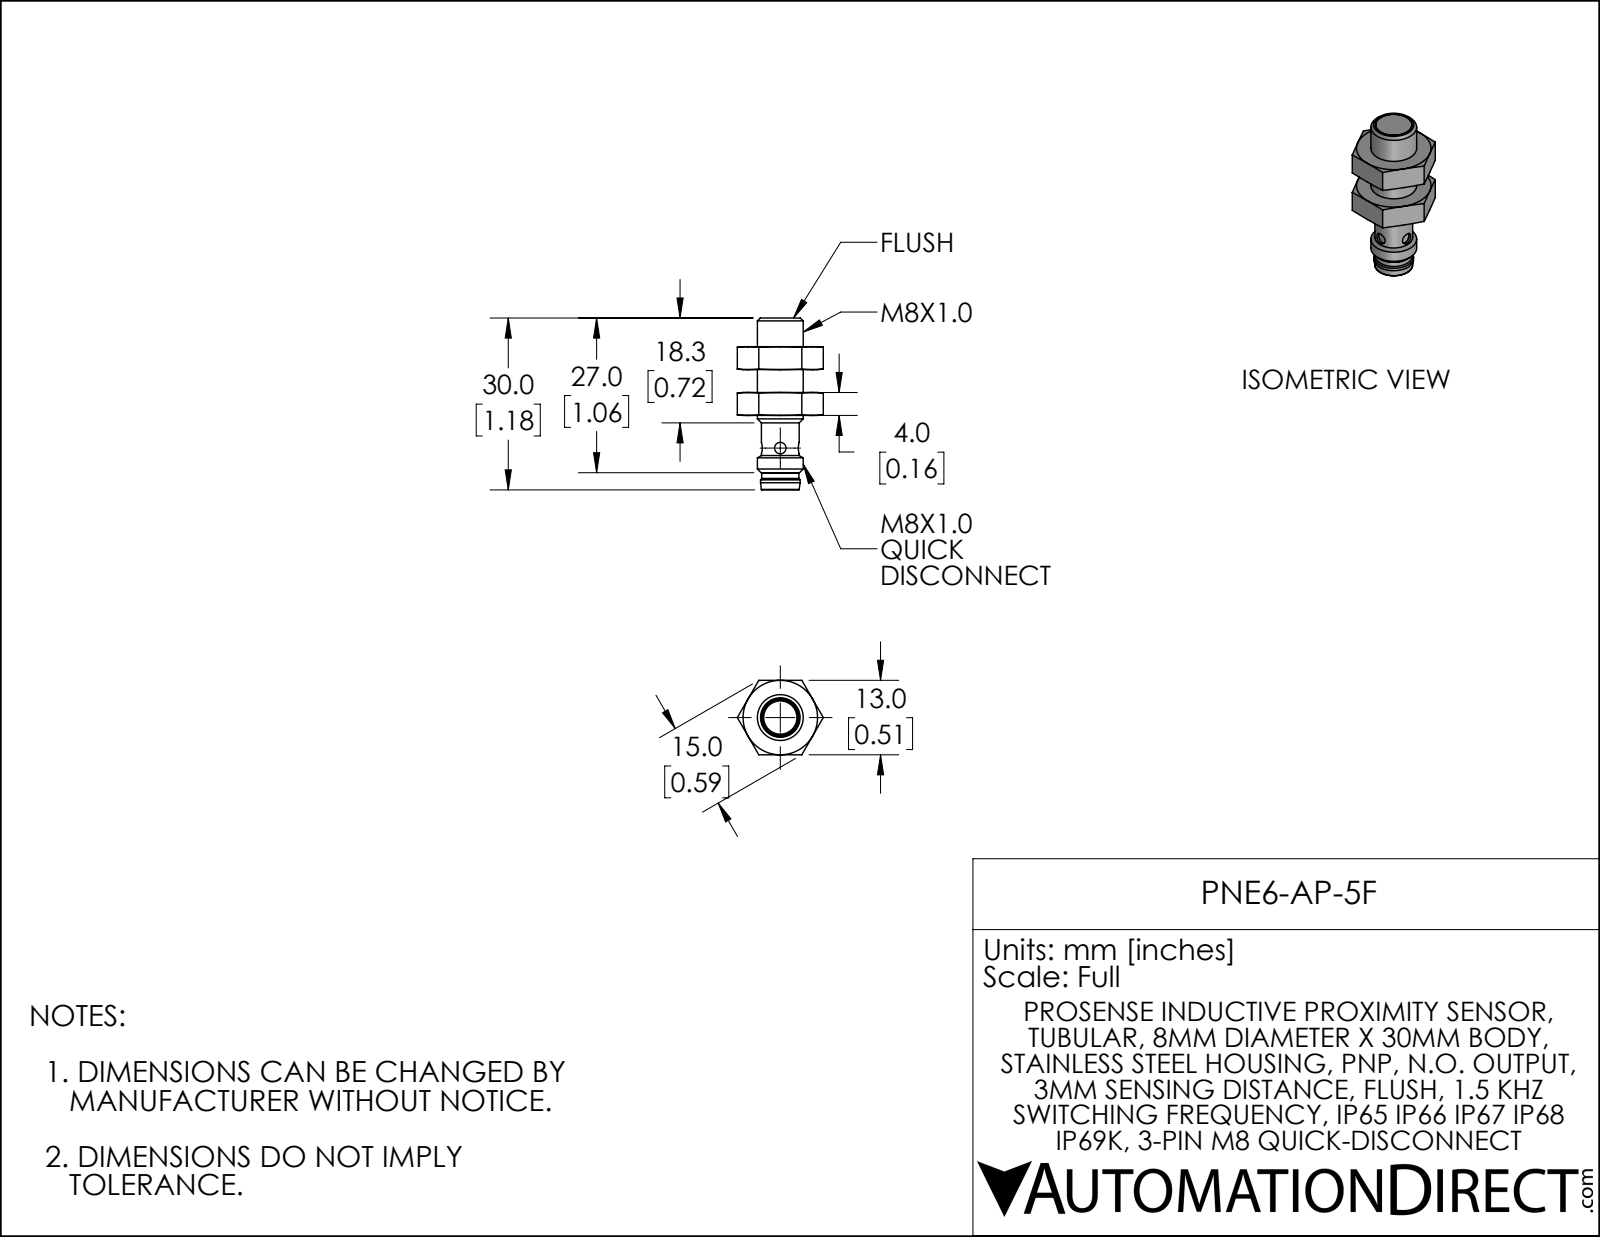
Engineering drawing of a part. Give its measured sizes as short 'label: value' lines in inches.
name: PNE6-AP-5F
written by: SolidWorks 2019 (CONFIG_CONTROL_DESIGN)
unit: in
bodies: 3 solids, 78 faces (23 planar, 19 cylindrical, 36 other)
size: 1.181 × 0.591 × 0.512
volume: 0.126 in³; area: 2.893 in²
holes: 2× ⌀0.079, 1× ⌀0.251, 1× ⌀0.272
bosses: 1× ⌀0.315, 1× ⌀0.272, 1× ⌀0.26, 1× ⌀0.256, 1× ⌀0.25, 1× ⌀0.248, 1× ⌀0.228
face distances: 0.512, 0.157, 0.315, 0.354, 0.197, 0.47, 0.628, 0.785, 0.982, 0.081
